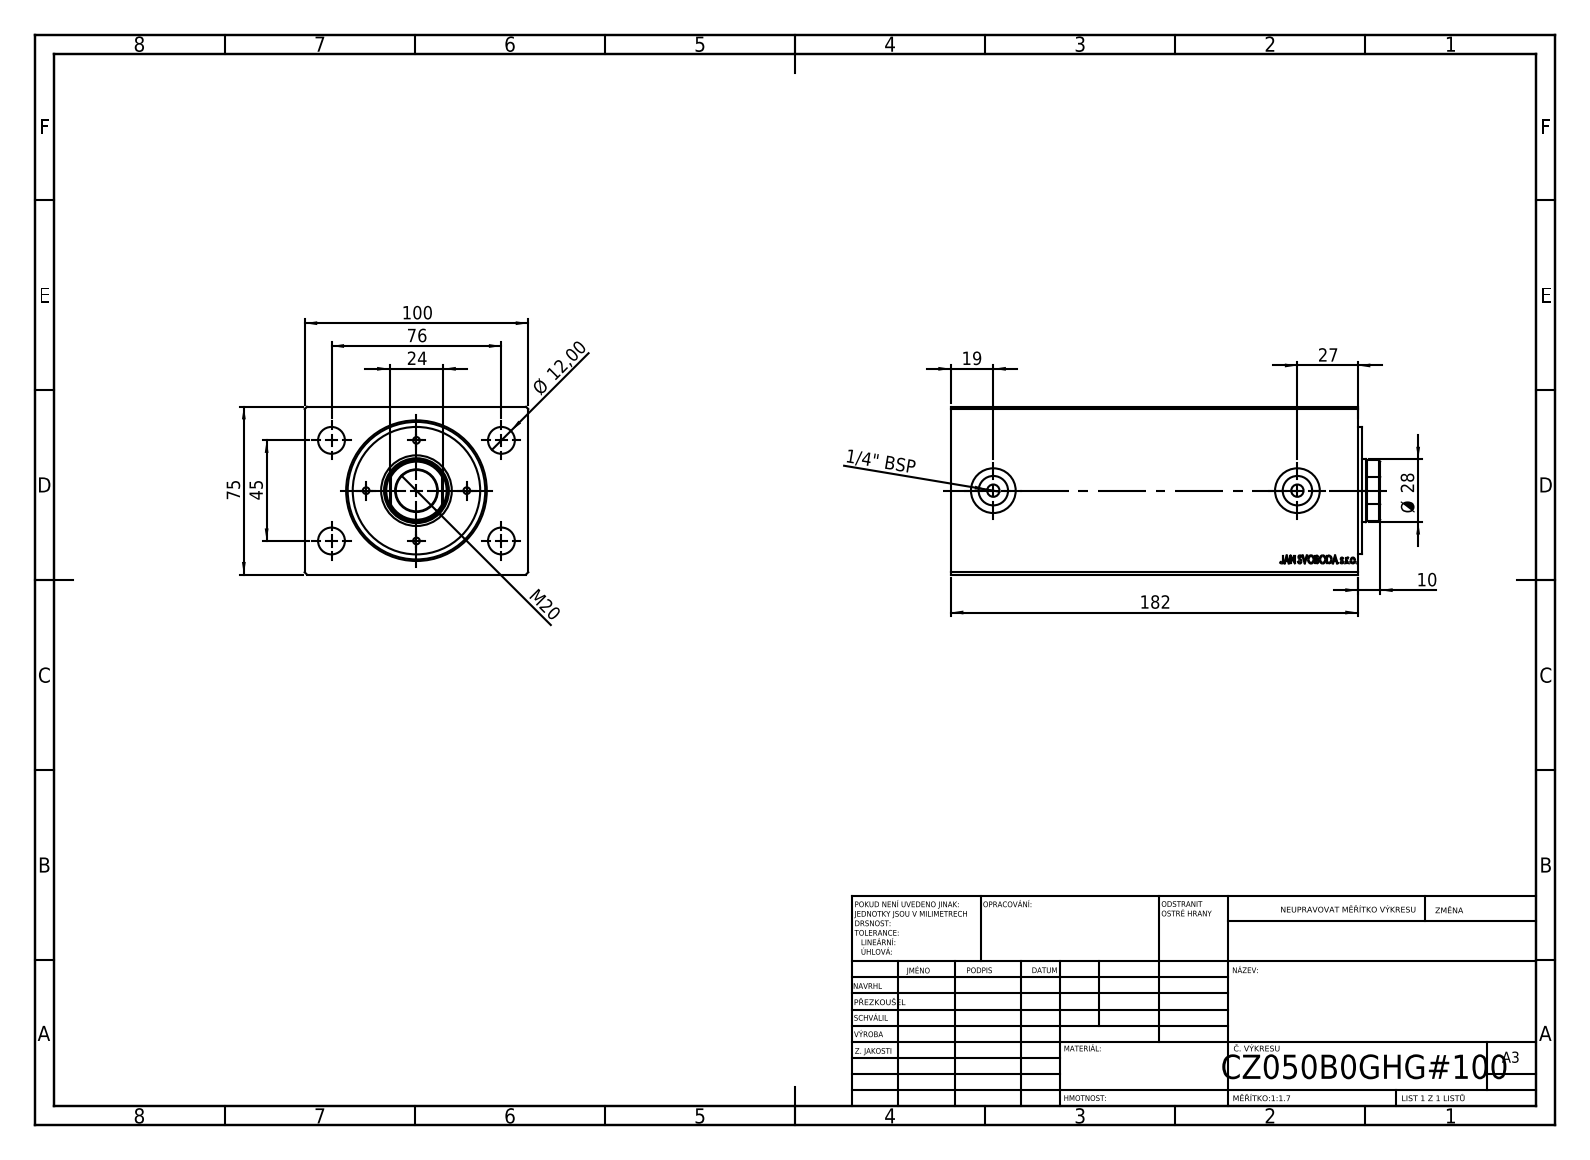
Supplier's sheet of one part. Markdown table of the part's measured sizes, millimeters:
| quantity | value |
| --- | --- |
| part name | V500CZ_B_VC; V500CZ |
| STEP written by | SolidWorks 2019 (CONFIG_CONTROL_DESIGN) |
| units | millimeters |
| bodies | 3 solids, 874 faces (400 planar, 58 cylindrical, 416 other) |
| overall size | 192 × 100 × 75 |
| volume | 1 199 000 mm³ |
| surface area | 145 469 mm² |
| round holes (diameter × count) | 3 × 4, 12 × 4, 5.5 × 2, 13.16 × 2, 20 × 2, 18.5 × 1, 28 × 1, 29 × 1, 36 × 1, 50 × 1, 61.5 × 1 |
| round bosses / shafts (diameter × count) | 57 × 1 |
| partial cylindrical surfaces (radius × count) | 13.5 × 1 |
| main face-to-face distances | 75, 100, 182, 164.2, 17.8, 10, 1.8, 8.2, 156, 173.8 |
| hole center spacings | 22.5, 27.32, 31.82, 38, 44.16, 45, 58.9, 64.55 |
